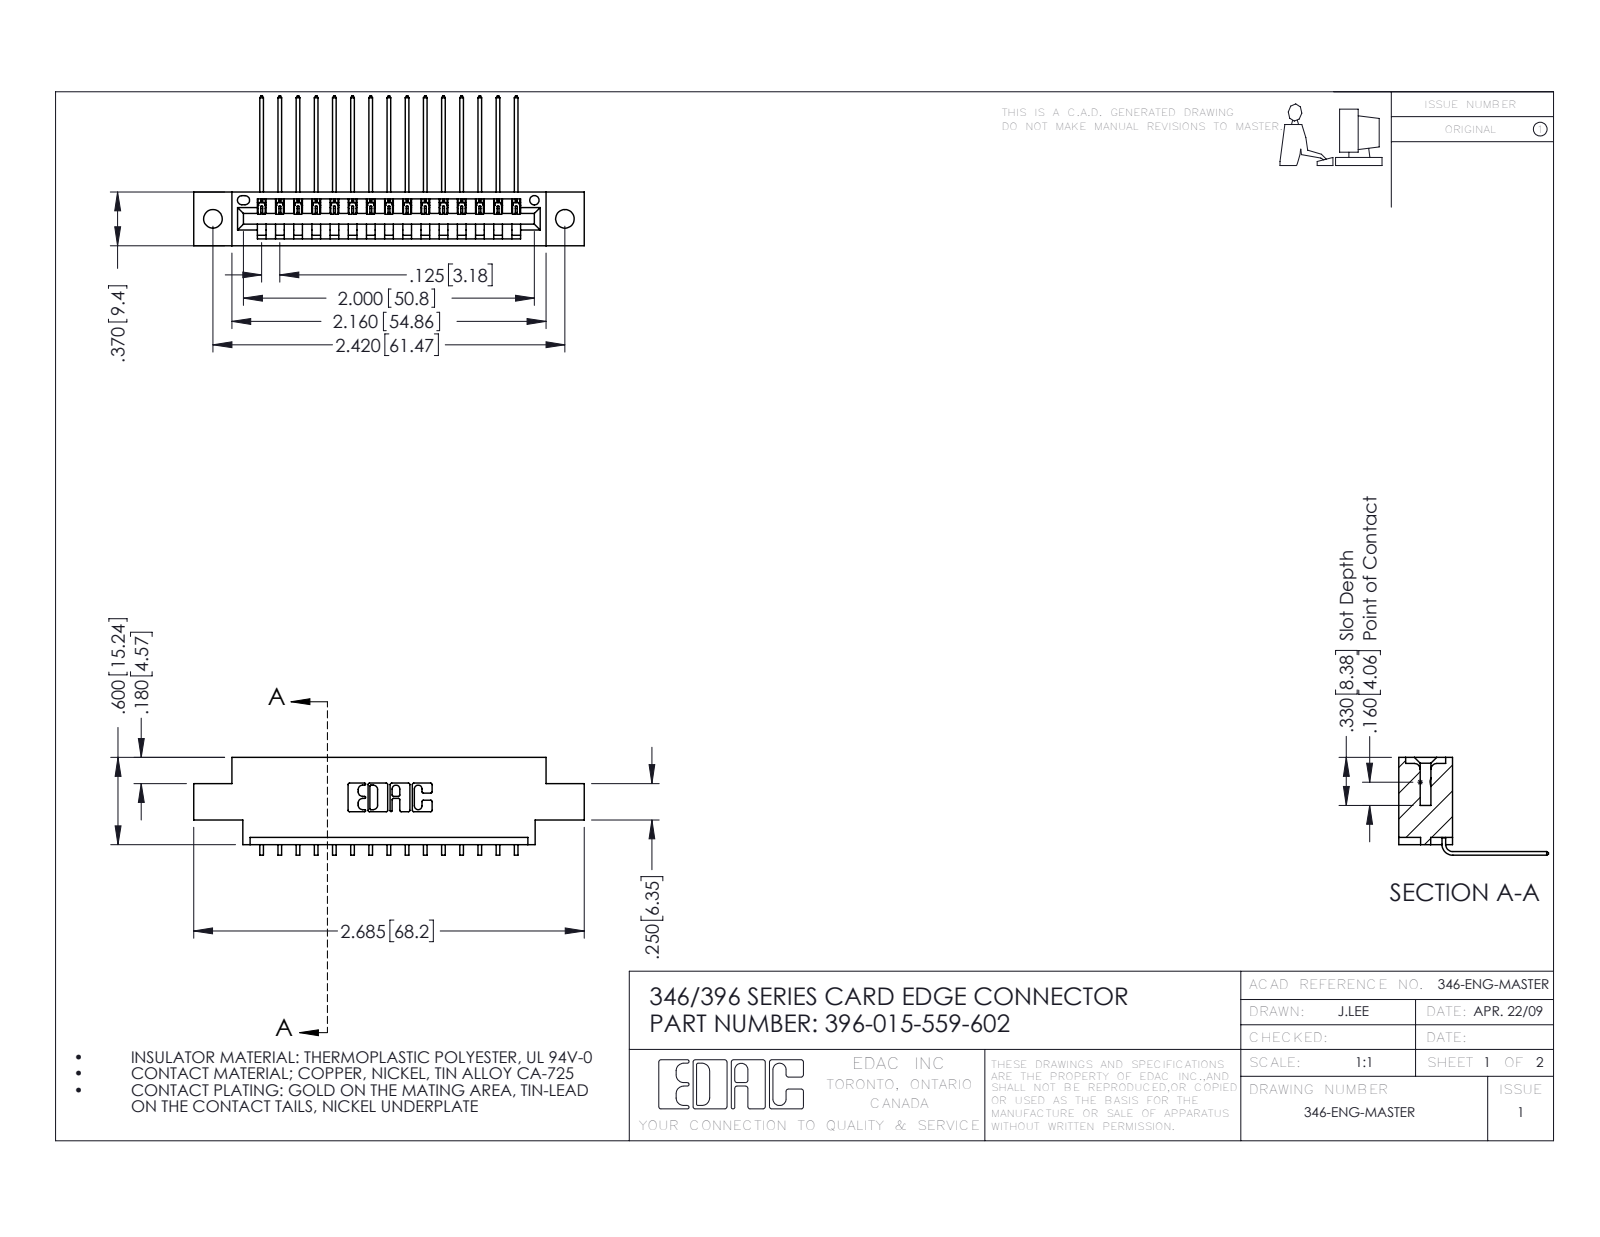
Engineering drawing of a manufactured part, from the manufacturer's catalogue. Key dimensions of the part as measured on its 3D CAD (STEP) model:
Part name (STEP PRODUCT): 346 Part_0.170 Offset - 0.128 Dia; 396-015-559-602; 345-292-001_558 559 Tail - 1
STEP written by: SolidWorks 2016 (CONFIG_CONTROL_DESIGN)
Units: inches
Bodies: 16 solids, 1026 faces (710 planar, 316 cylindrical, 0 other)
Overall size (bounding box): 2.685 × 1.03 × 0.673
Volume: 0.378 in³ · Surface area: 11.85 in²
Round holes (diameter × count): ⌀0.128 ×2, ⌀0.064 ×1
Partial cylindrical surfaces — rounded edges, fillets, slot ends (radius × count): R0.006 ×30, R0.01 ×22, R0.007 ×6, R0.031 ×6, R0.026 ×3, R0.031 ×2, R0.04 ×2, R0.014 ×1
Main face-to-face distances: 0.048, 0.37, 0.322, 0.25, 0.025, 0.072, 0.148, 0.222, 0.1, 0.174
Hole centre spacings: 0.246, 2.213, 2.42
